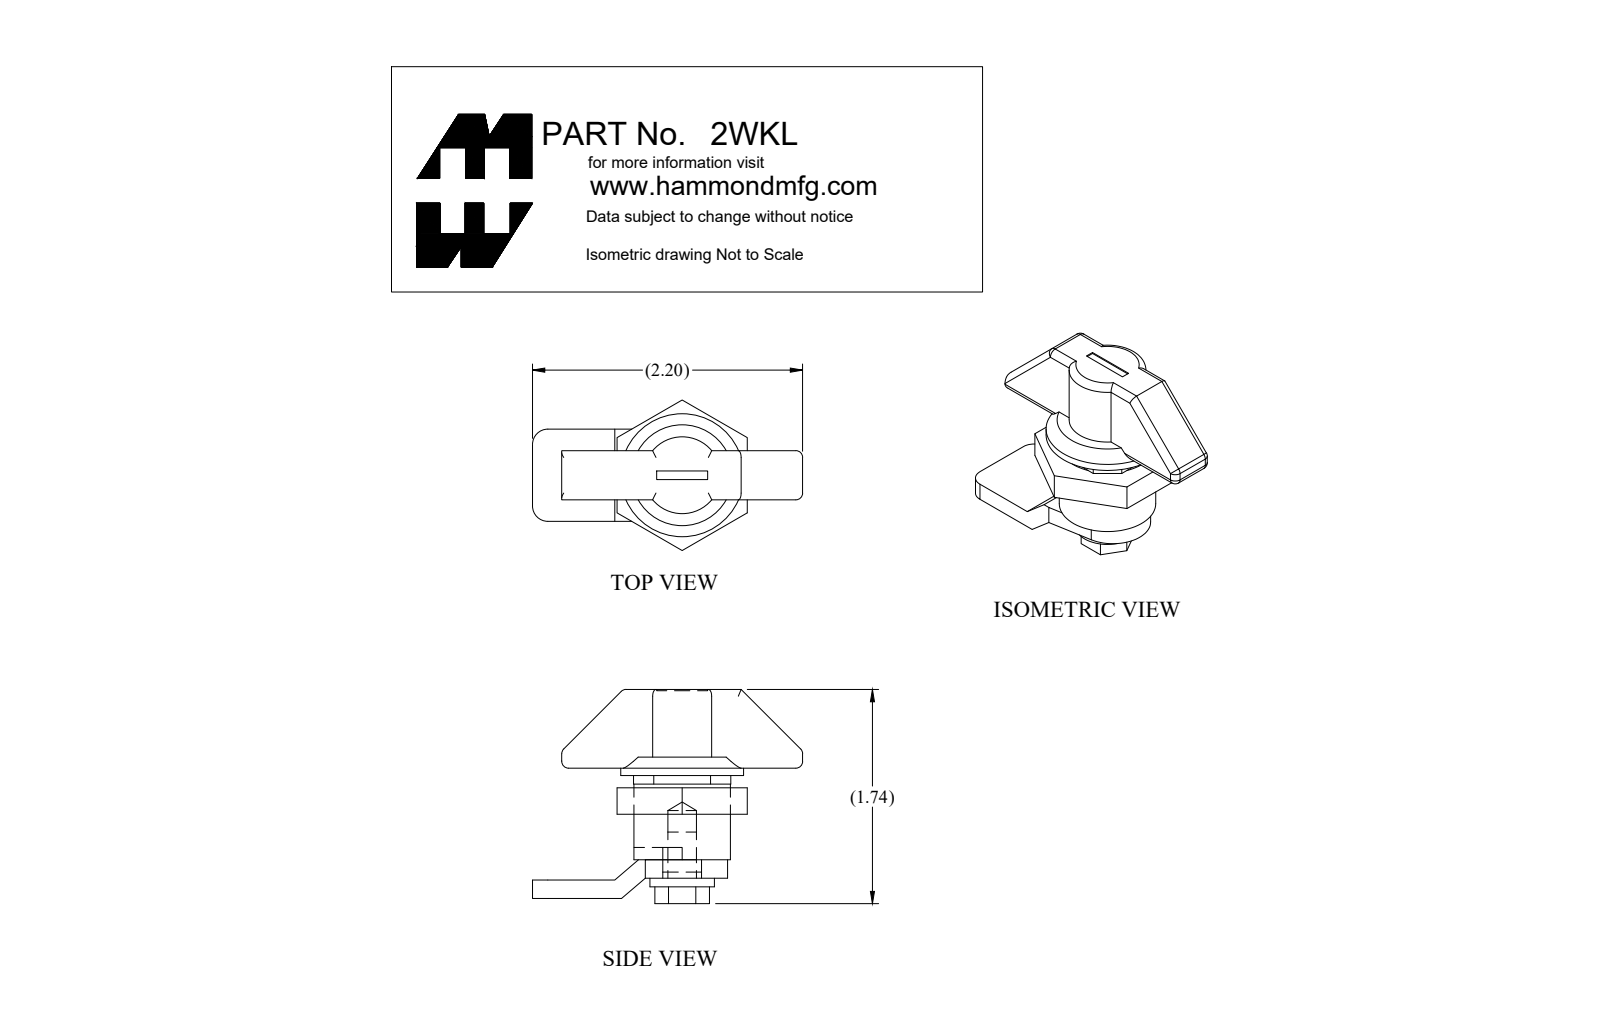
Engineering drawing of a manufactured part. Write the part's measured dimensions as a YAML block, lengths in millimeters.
part_name: "2WKL"
step_written_by: "SolidWorks 2018 (AUTOMOTIVE_DESIGN)"
units: millimeters
bodies: {solids: 4, faces: 111, planar: 70, cylindrical: 30, other: 11}
overall_size: [55.8, 44.2, 31.1]
volume: 18600
surface_area: 8432
round_holes:
  - {diameter: 5.9, count: 1}
  - {diameter: 19.9, count: 1}
round_bosses_or_shafts:
  - {diameter: 25.4, count: 1}
  - {diameter: 13.3, count: 1}
partial_cylinders:
  - {radius: 1.4, count: 15}
  - {radius: 3.2, count: 2}
  - {radius: 7.8, count: 1}
  - {radius: 8, count: 1}
face_to_face_distances: [3.8, 4.2, 8, 17.4, 26.9, 14.9, 18.7, 5.5, 10.2, 22.9]
